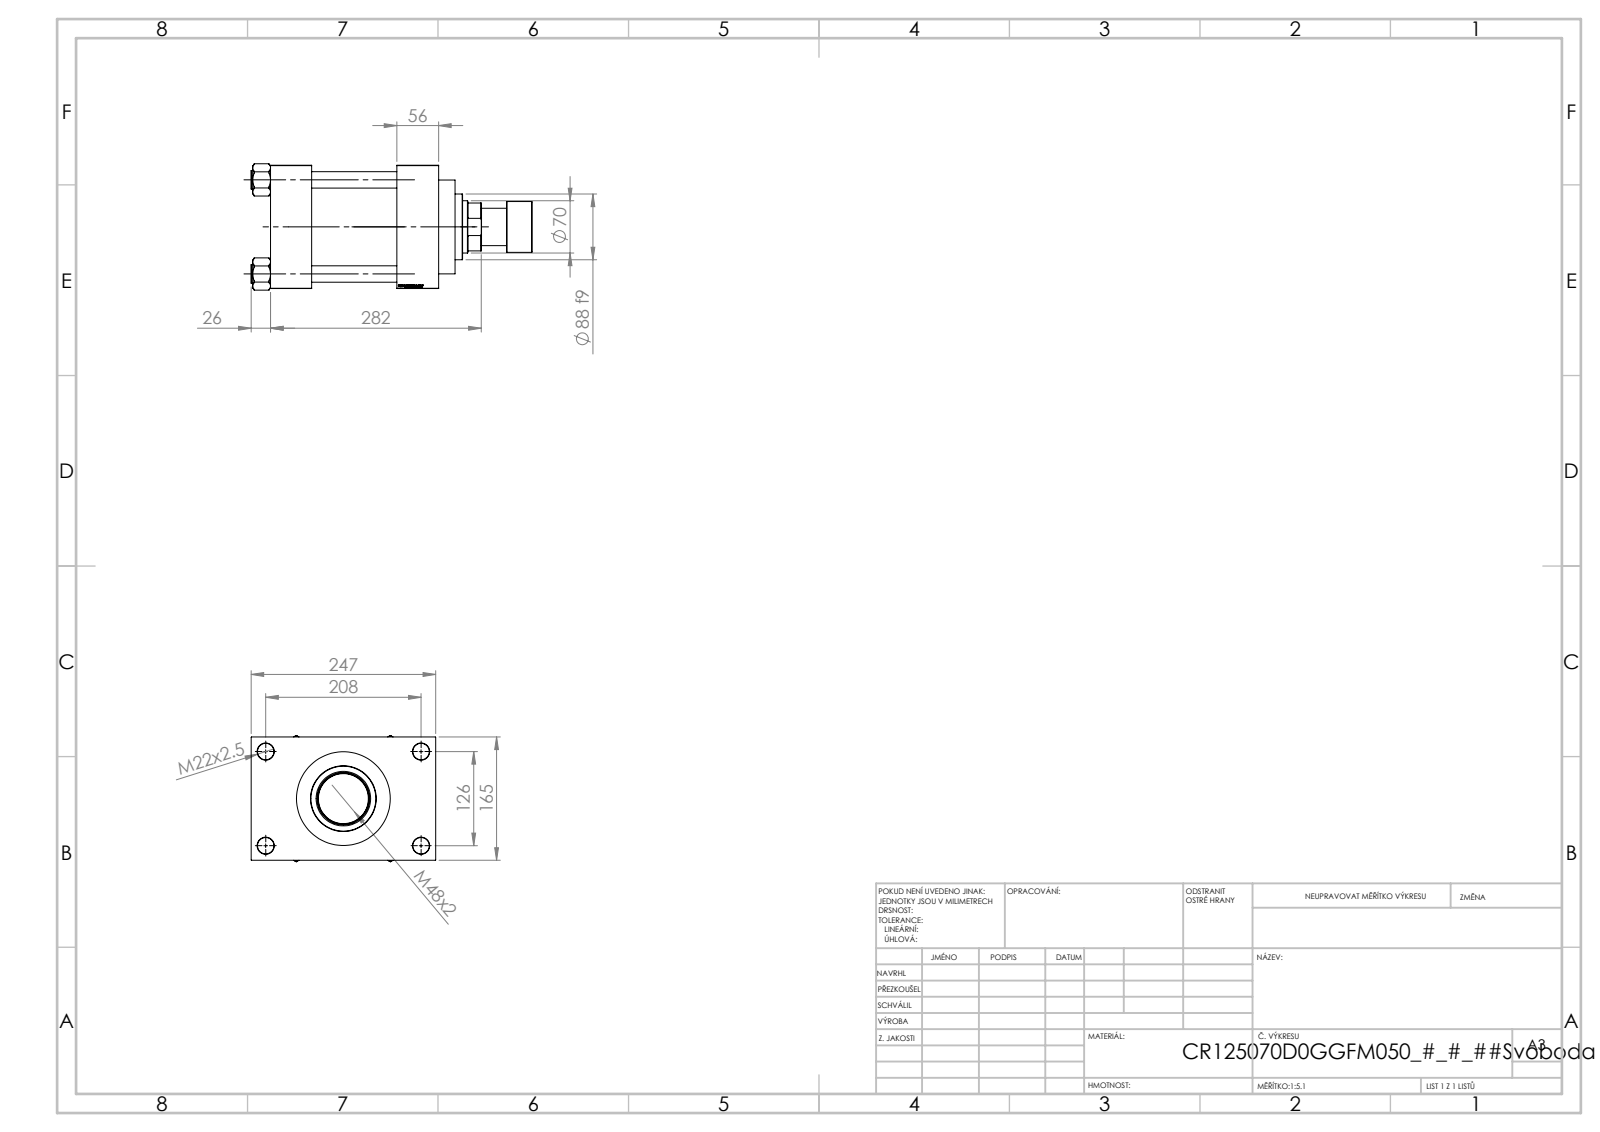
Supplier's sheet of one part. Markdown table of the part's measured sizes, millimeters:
| quantity | value |
| --- | --- |
| part name | V215CR_VCP_D; V215CR_D_TYCINKA; NUT_M5_D; V215CR_D_Body (+2 more) |
| STEP written by | SolidWorks 2019 (CONFIG_CONTROL_DESIGN) |
| units | millimeters |
| bodies | 12 solids, 1163 faces (548 planar, 93 cylindrical, 522 other) |
| overall size | 376 × 247 × 169.14 |
| volume | 5 434 000 mm³ |
| surface area | 596 794 mm² |
| round holes (diameter × count) | 22 × 8, 7 × 2, 32.24 × 2, 45 × 2, 46.5 × 1, 70 × 1, 73 × 1, 96 × 1, 125 × 1, 125.5 × 1 |
| round bosses / shafts (diameter × count) | 25 × 4, 131 × 1, 88 × 1, 68 × 1, 50 × 1, 49 × 1 |
| main face-to-face distances | 114, 165, 55, 169, 225, 170, 56, 41, 206, 247 |
| hole center spacings | 41.05, 89.02, 121.59, 125.9, 132.47, 166.95, 209.13, 126 |
